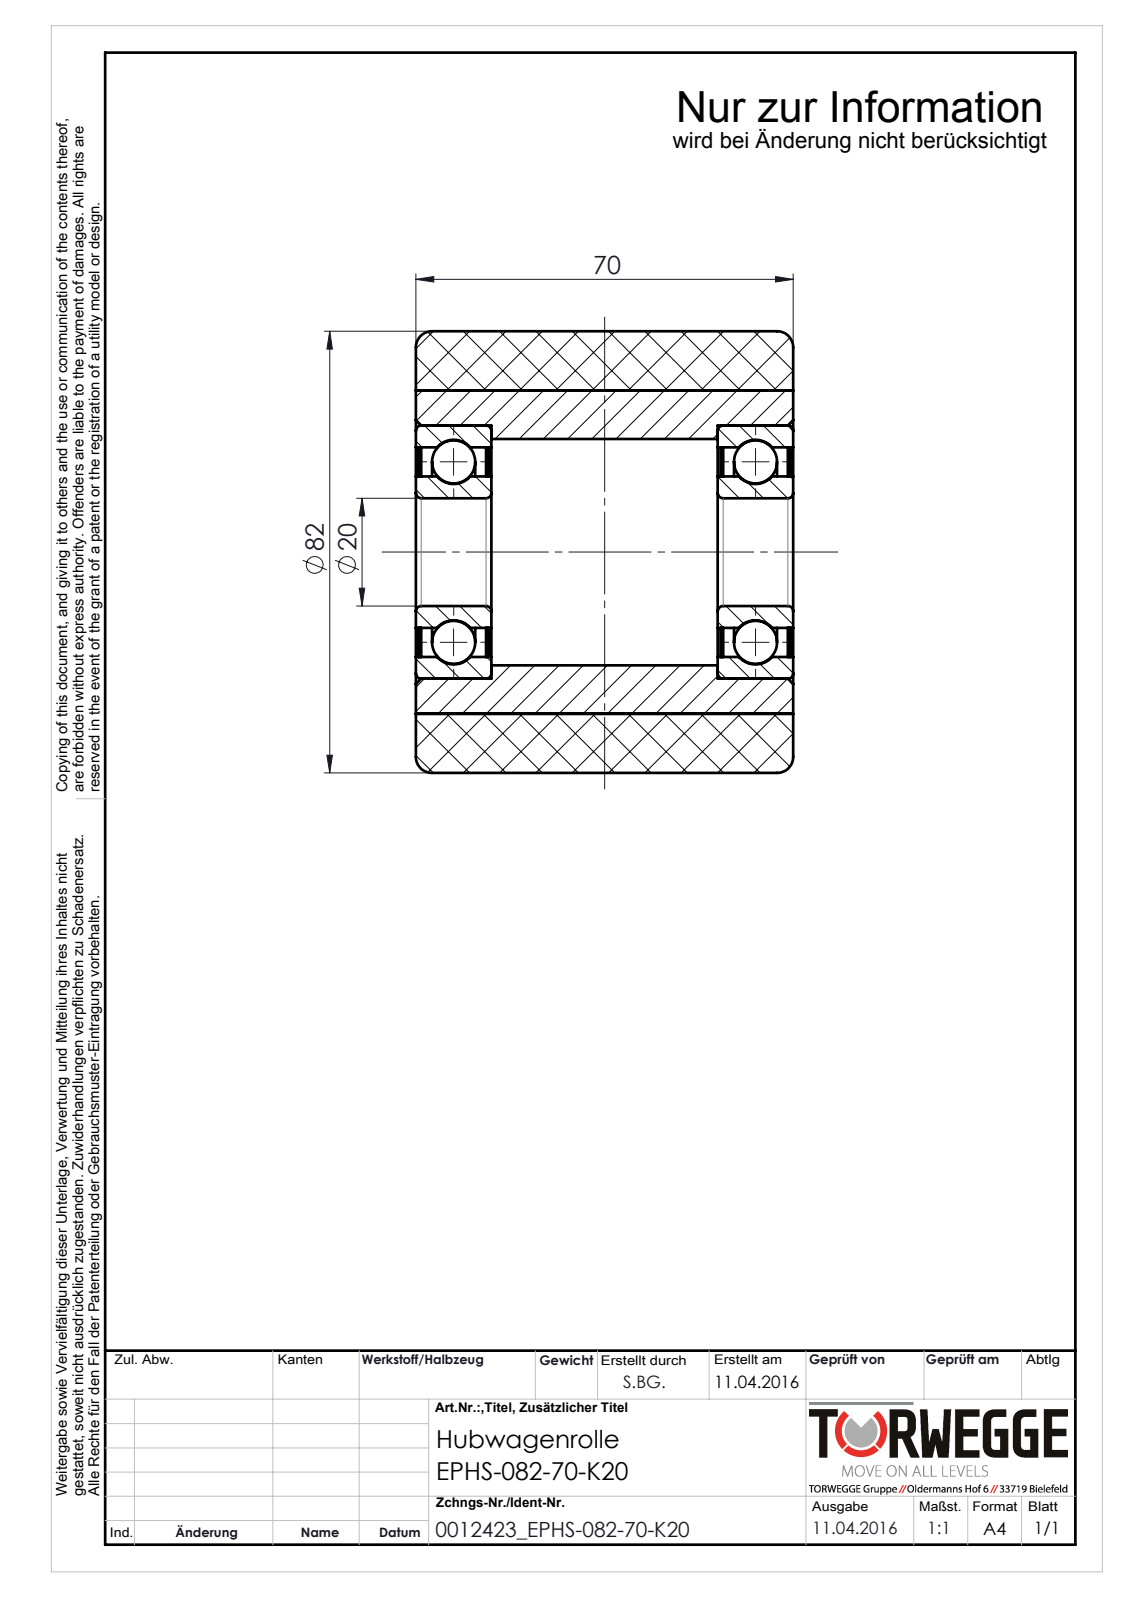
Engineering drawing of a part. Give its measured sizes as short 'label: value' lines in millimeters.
name: 0012423_EPHS-082-70-K20
written by: SolidWorks 2016 (AUTOMOTIVE_DESIGN)
unit: mm
bodies: 12 solids, 118 faces (22 planar, 52 cylindrical, 44 other)
size: 82 × 82 × 70
volume: 294 659 mm³; area: 86 484 mm²
holes: 1× ⌀20, 1× ⌀28.1, 1× ⌀38.9, 1× ⌀42, 1× ⌀47, 1× ⌀60
bosses: 1× ⌀82
face distances: 0.5, 56, 13, 70, 1, 13.5, 56.5, 55.5, 12.5, 14
